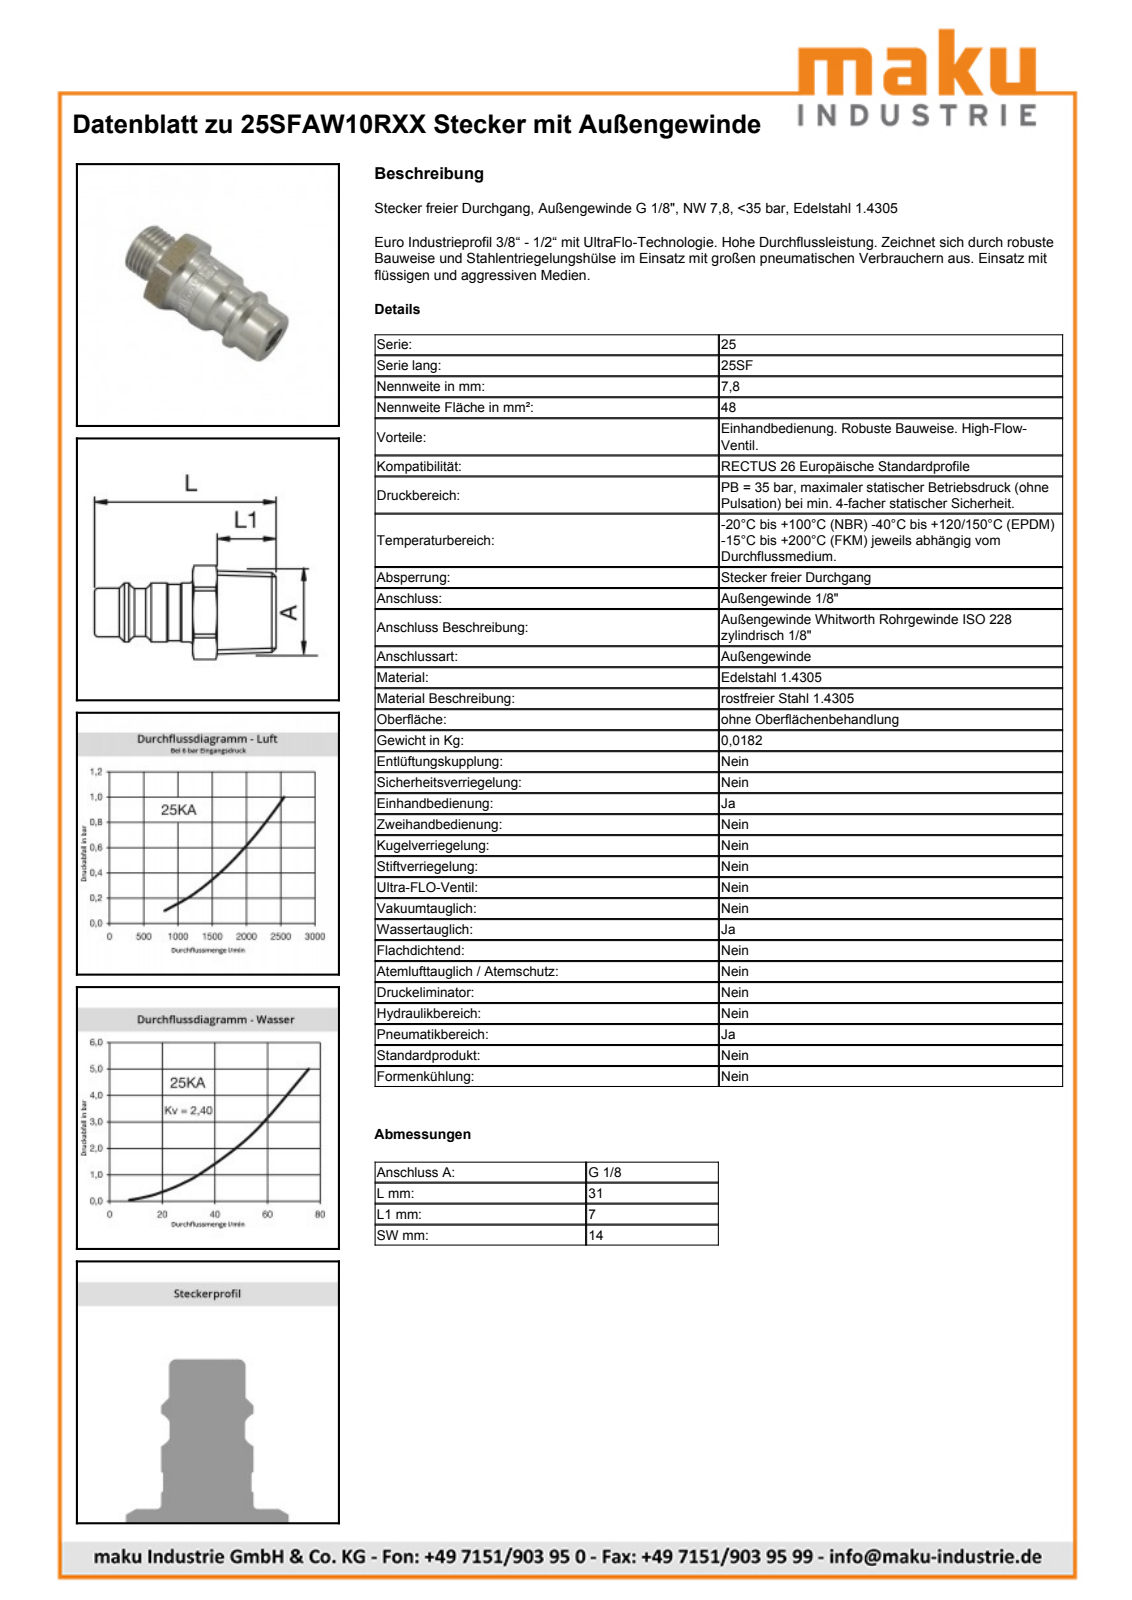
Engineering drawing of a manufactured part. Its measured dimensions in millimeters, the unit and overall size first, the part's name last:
Units: millimetres
Overall size (bounding box): 31 × 15.8 × 14
Round bosses / shafts (diameter × count): ⌀12 ×1, ⌀9.9 ×1, ⌀9.75 ×1, ⌀9.73 ×1
Partial cylindrical surfaces — rounded edges, fillets, slot ends (radius × count): R7.9 ×1
Main face-to-face distances: 14, 7, 24, 31, 20, 4, 11
Volume: 3 078 mm³ · Surface area: 1 414 mm²
Bodies: 1 solid, 42 faces (10 planar, 11 cylindrical, 21 other)
Part name (STEP PRODUCT): D103713
STEP written by: Autodesk Inventor 2011 (AUTOMOTIVE_DESIGN)
